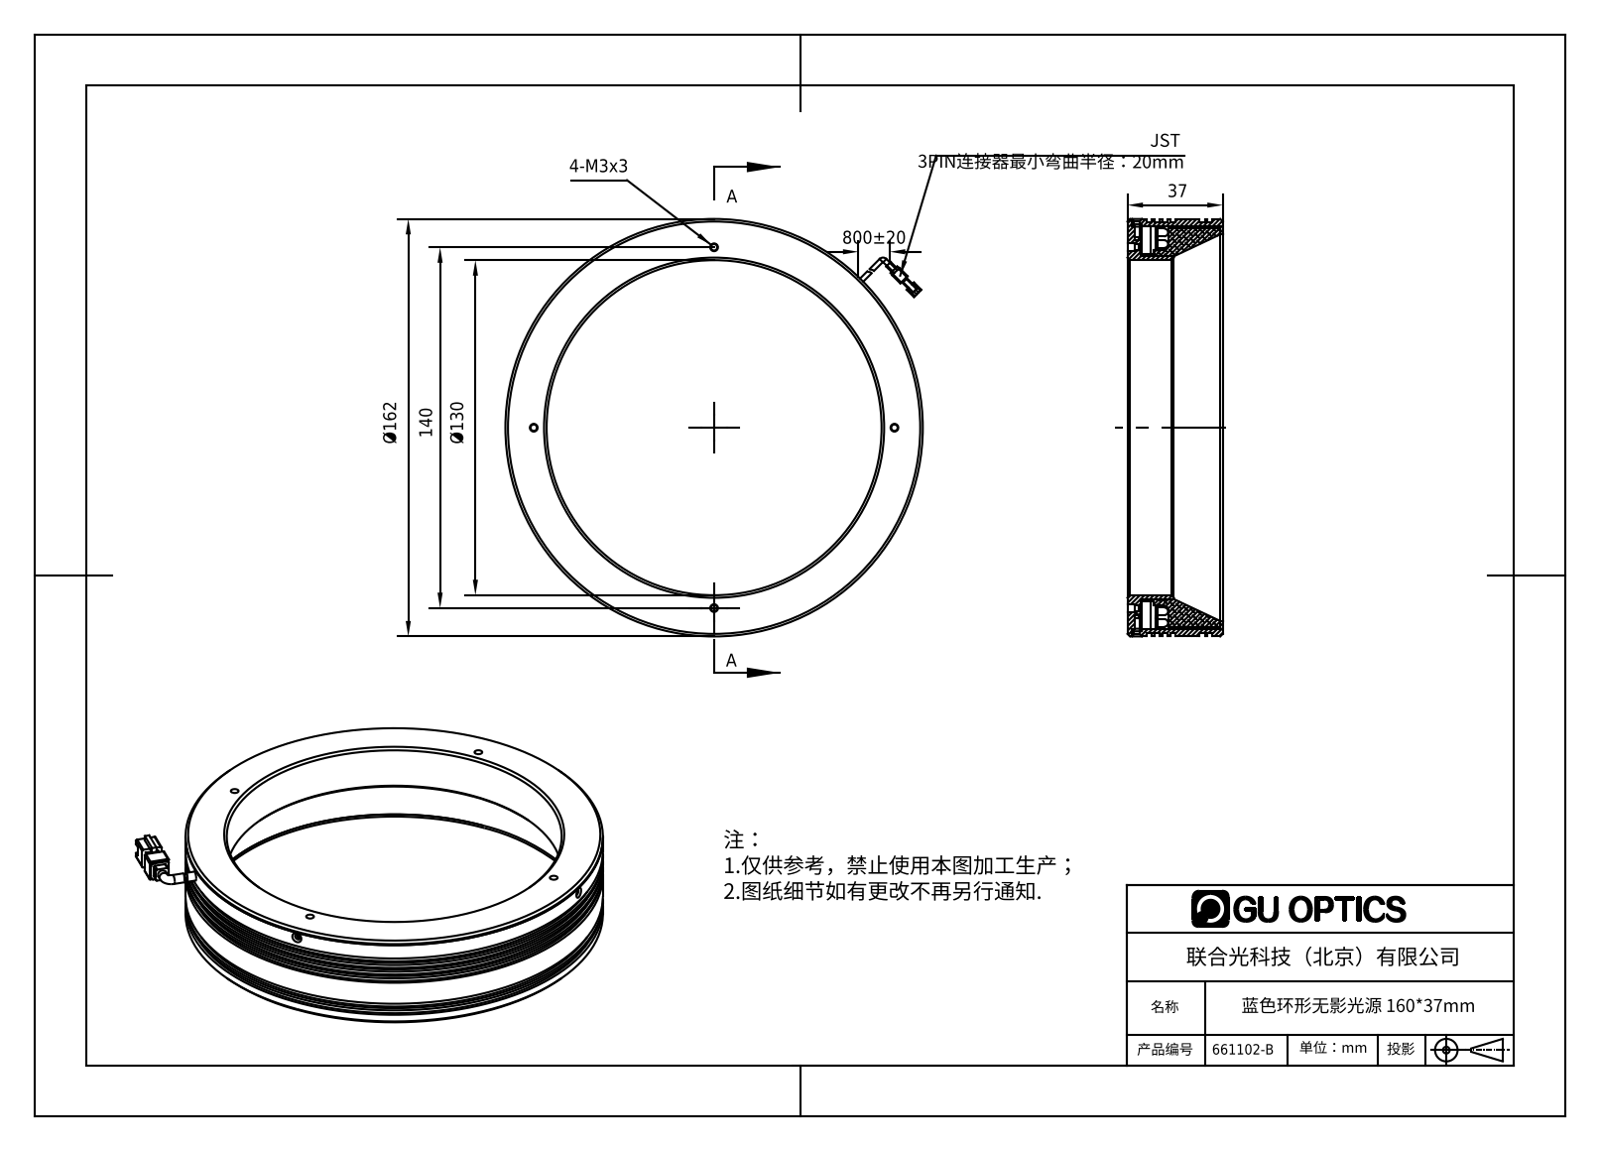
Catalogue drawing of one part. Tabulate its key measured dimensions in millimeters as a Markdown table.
| quantity | value |
| --- | --- |
| part name | 661102-B |
| STEP written by | SolidWorks 2016 (AUTOMOTIVE_DESIGN) |
| units | millimeters |
| bodies | 5 solids, 260 faces (91 planar, 129 cylindrical, 40 other) |
| overall size | 168.11 × 162 × 38.5 |
| volume | 159 756 mm³ |
| surface area | 113 568 mm² |
| round holes (diameter × count) | 2.5 × 4, 3 × 4, 1.6 × 2, 2 × 2, 2.4 × 2, 130 × 1, 133 × 1, 150 × 1, 158 × 1 |
| round bosses / shafts (diameter × count) | 3.5 × 2, 162 × 1, 159.6 × 1, 156 × 1, 155 × 1, 138 × 1, 135 × 1 |
| partial cylindrical surfaces (radius × count) | 0.5 × 8, 1 × 4, 6 × 1 |
| main face-to-face distances | 5, 3, 14.5, 6, 1, 11, 2, 3.5, 20.5, 20 |
| hole center spacings | 70, 98.99, 140 |
